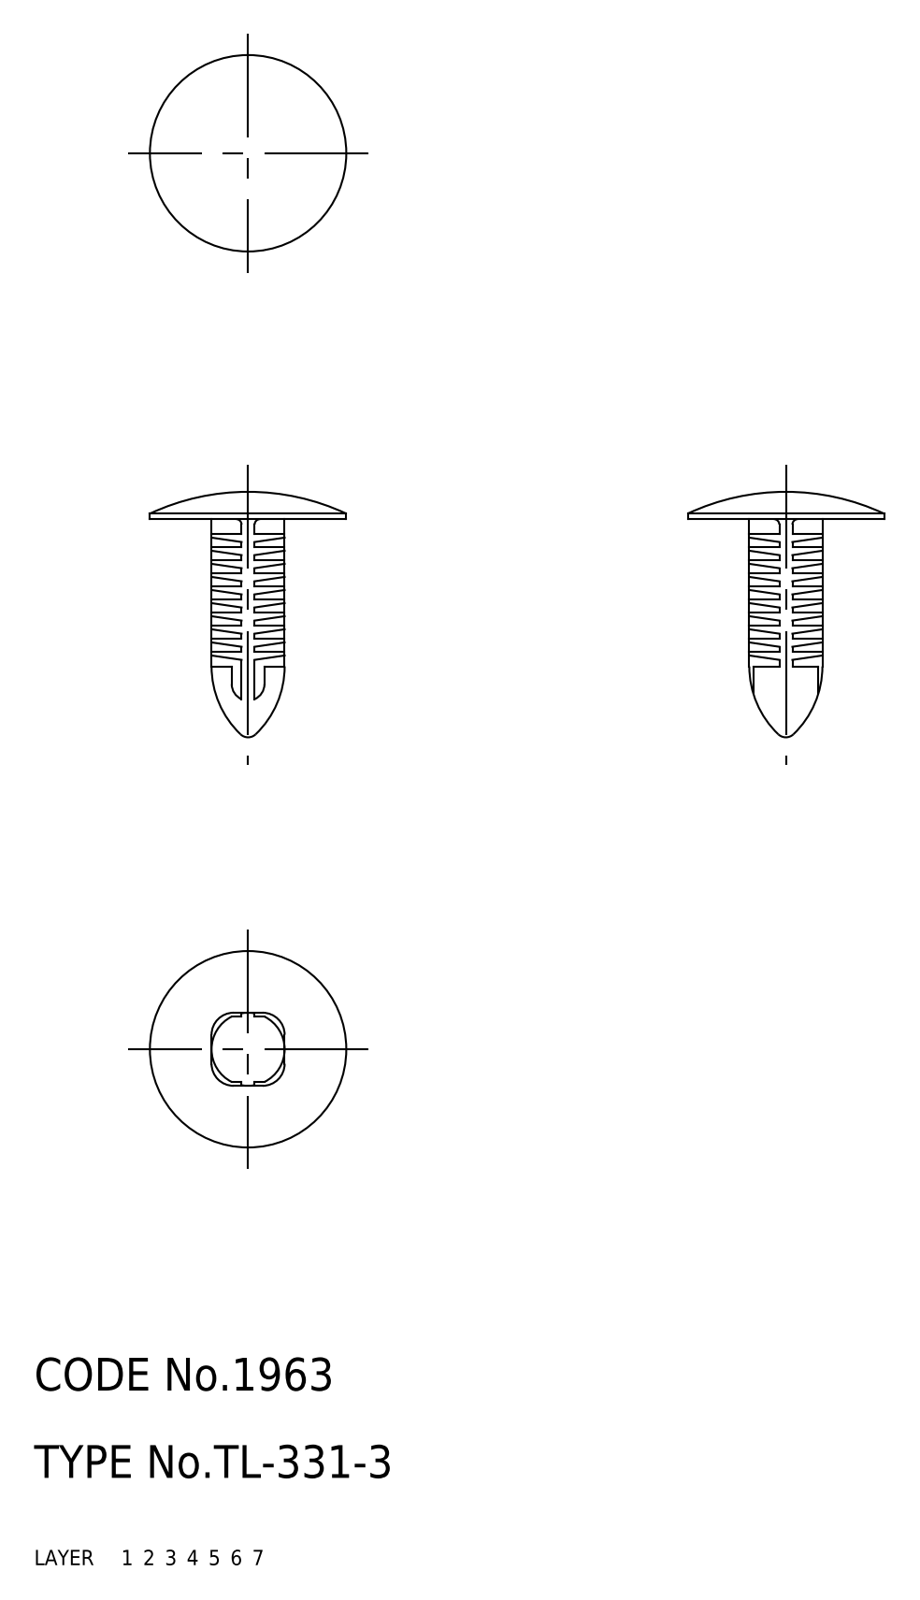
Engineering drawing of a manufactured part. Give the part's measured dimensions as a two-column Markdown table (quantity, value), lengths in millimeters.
| quantity | value |
| --- | --- |
| part name | fastener |
| STEP written by | CADfix (AUTOMOTIVE_DESIGN) |
| units | millimeters |
| bodies | 1 solid, 311 faces (0 planar, 0 cylindrical, 311 other) |
| overall size | 22.5 × 18 × 18 |
| volume | 884 mm³ |
| surface area | 1 586 mm² |
